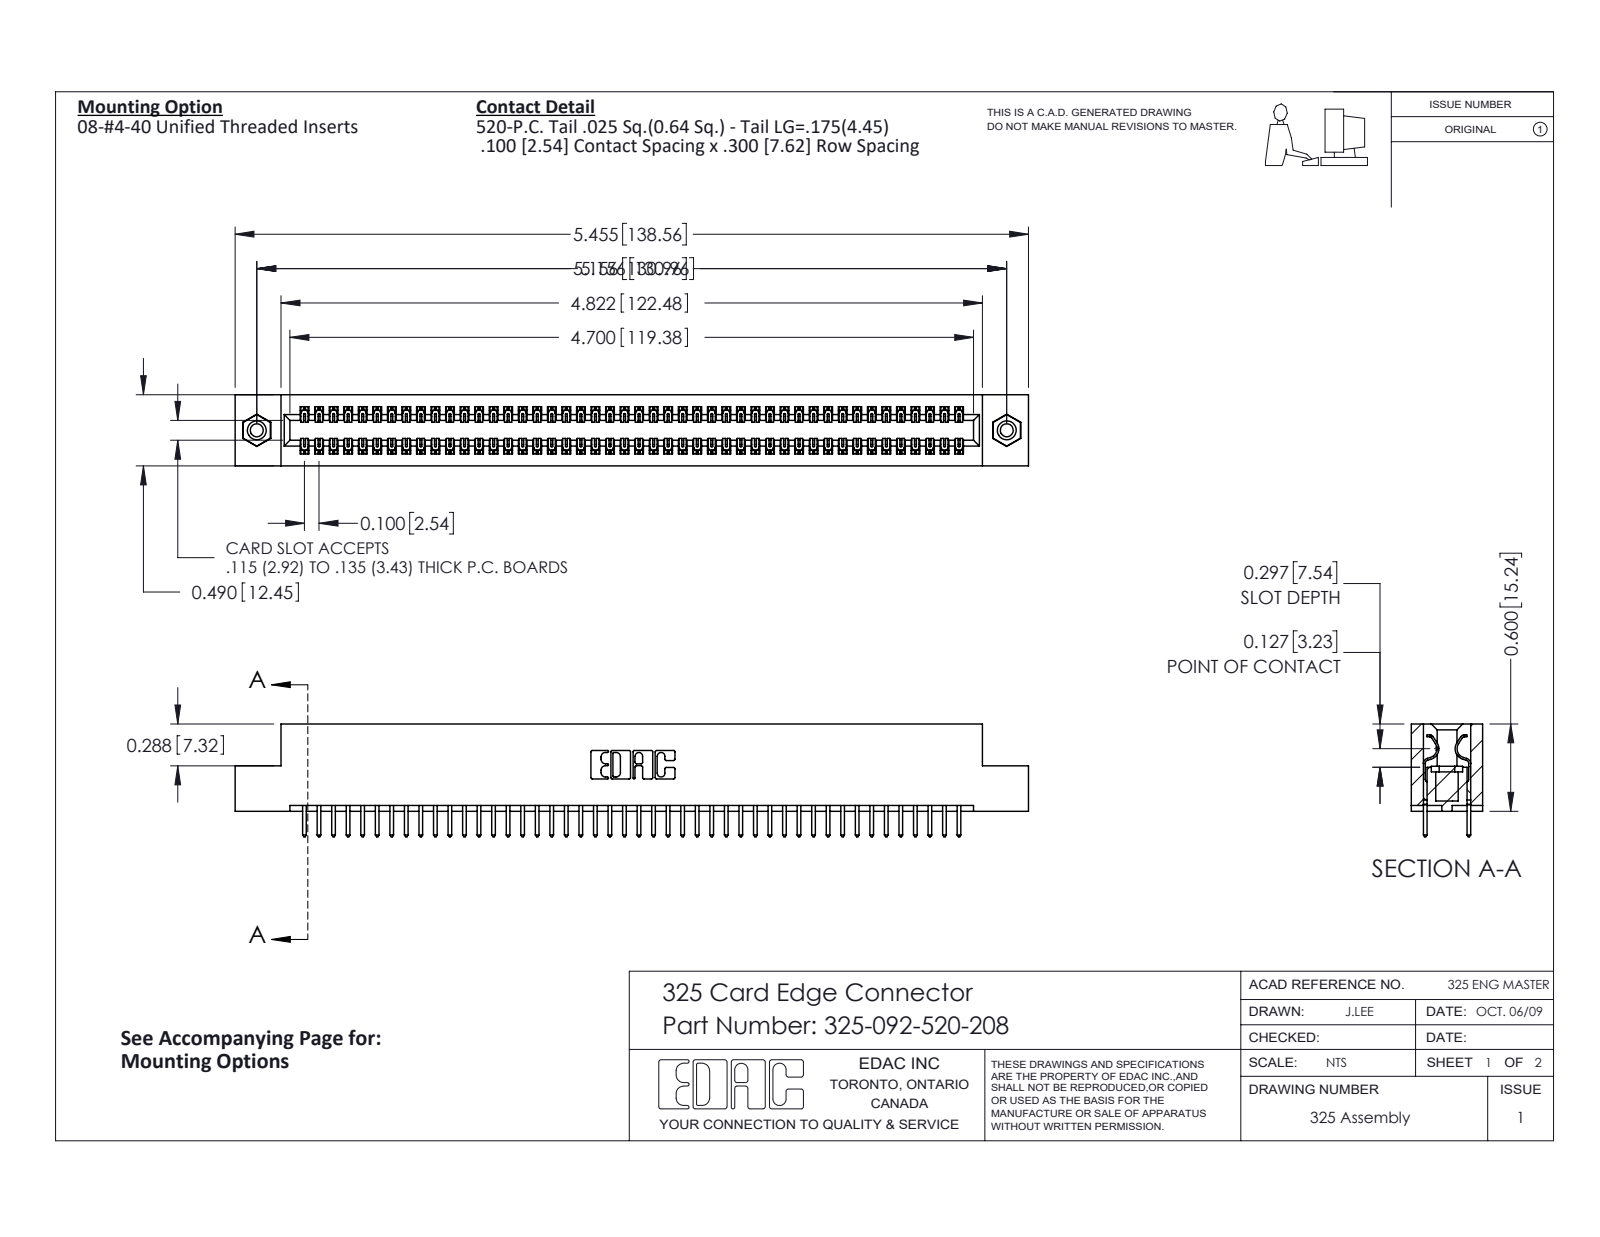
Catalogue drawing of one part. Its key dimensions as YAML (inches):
part_name: "325-092-520-208; 345-250-001_345-250-003-102; 325-292-001_325-293-120; 325 Part_TI"
step_written_by: "SolidWorks 2016 (CONFIG_CONTROL_DESIGN)"
units: inches
bodies: {solids: 95, faces: 4958, planar: 3414, cylindrical: 1528, other: 16}
overall_size: [5.455, 0.775, 0.49]
volume: 1.092
surface_area: 33.47
round_holes:
  - {diameter: 0.089, count: 2}
  - {diameter: 0.125, count: 2}
  - {diameter: 0.16, count: 2}
round_bosses_or_shafts:
  - {diameter: 0.155, count: 2}
partial_cylinders:
  - {radius: 0.006, count: 138}
  - {radius: 0.01, count: 92}
  - {radius: 0.01, count: 22}
  - {radius: 0.007, count: 6}
  - {radius: 0.031, count: 6}
  - {radius: 0.026, count: 3}
  - {radius: 0.014, count: 2}
  - {radius: 0.022, count: 2}
face_to_face_distances: [0.083, 0.407, 0.3, 0.49, 0.107, 0.383, 0.025, 0.325, 0.275, 0.56]
hole_center_spacings: [5.156]
